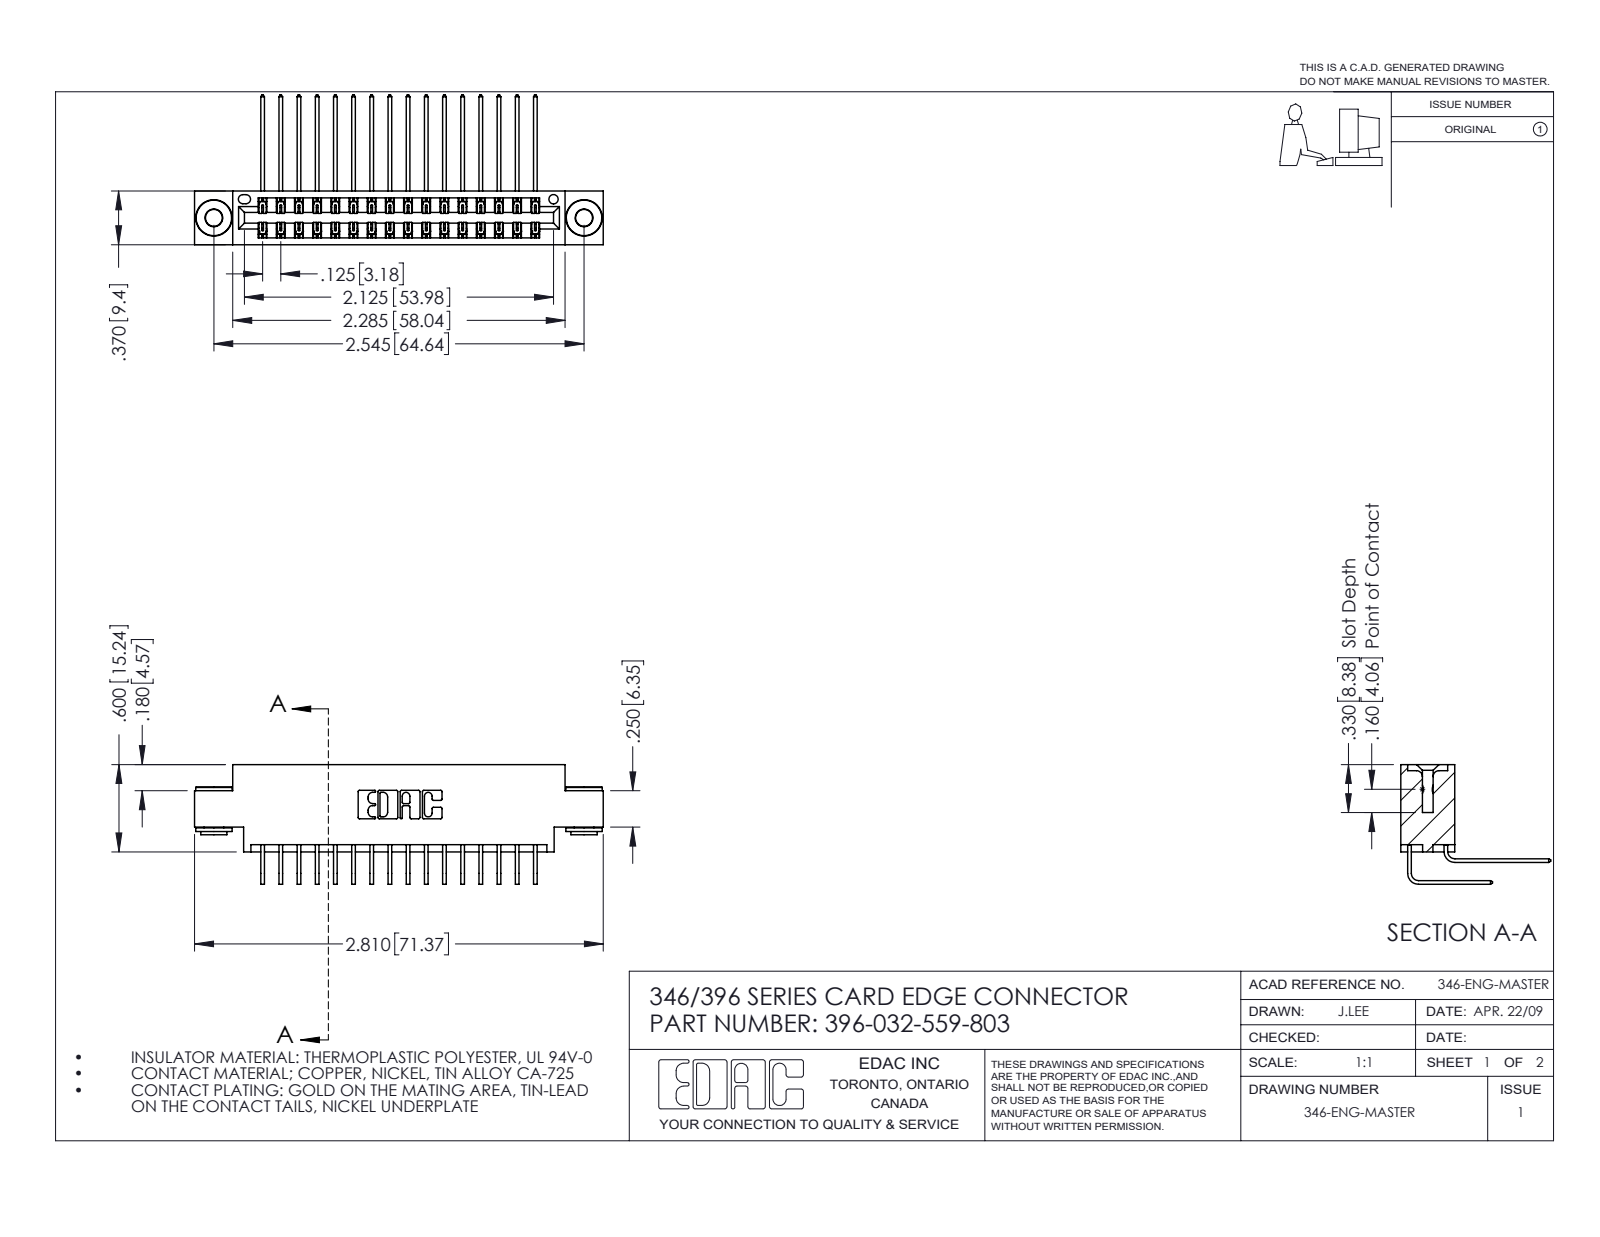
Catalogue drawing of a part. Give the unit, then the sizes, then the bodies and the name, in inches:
Units: inches
Overall size (bounding box): 2.81 × 1.03 × 0.823
Round holes (diameter × count): ⌀0.116 ×2, ⌀0.156 ×2, ⌀0.064 ×1
Round bosses / shafts (diameter × count): ⌀0.25 ×2, ⌀0.18 ×2, ⌀0.136 ×2
Partial cylindrical surfaces — rounded edges, fillets, slot ends (radius × count): R0.006 ×48, R0.01 ×22, R0.007 ×6, R0.031 ×6, R0.026 ×3, R0.014 ×2, R0.022 ×2, R0.024 ×2
Main face-to-face distances: 0.048, 0.322, 0.37, 0.25, 0.025, 0.072, 0.298, 0.275, 0.15, 0.148
Hole centre spacings: 0.246, 2.338, 2.545
Volume: 0.415 in³ · Surface area: 15.85 in²
Bodies: 35 solids, 1892 faces (1274 planar, 610 cylindrical, 8 other)
Part name (STEP PRODUCT): 345-292-001_559 Tail - 2; 396-032-559-803; 345-292-001_558 559 Tail - 1; 345-250-002_345-250-002-102 (+1 more)
STEP written by: SolidWorks 2016 (CONFIG_CONTROL_DESIGN)
